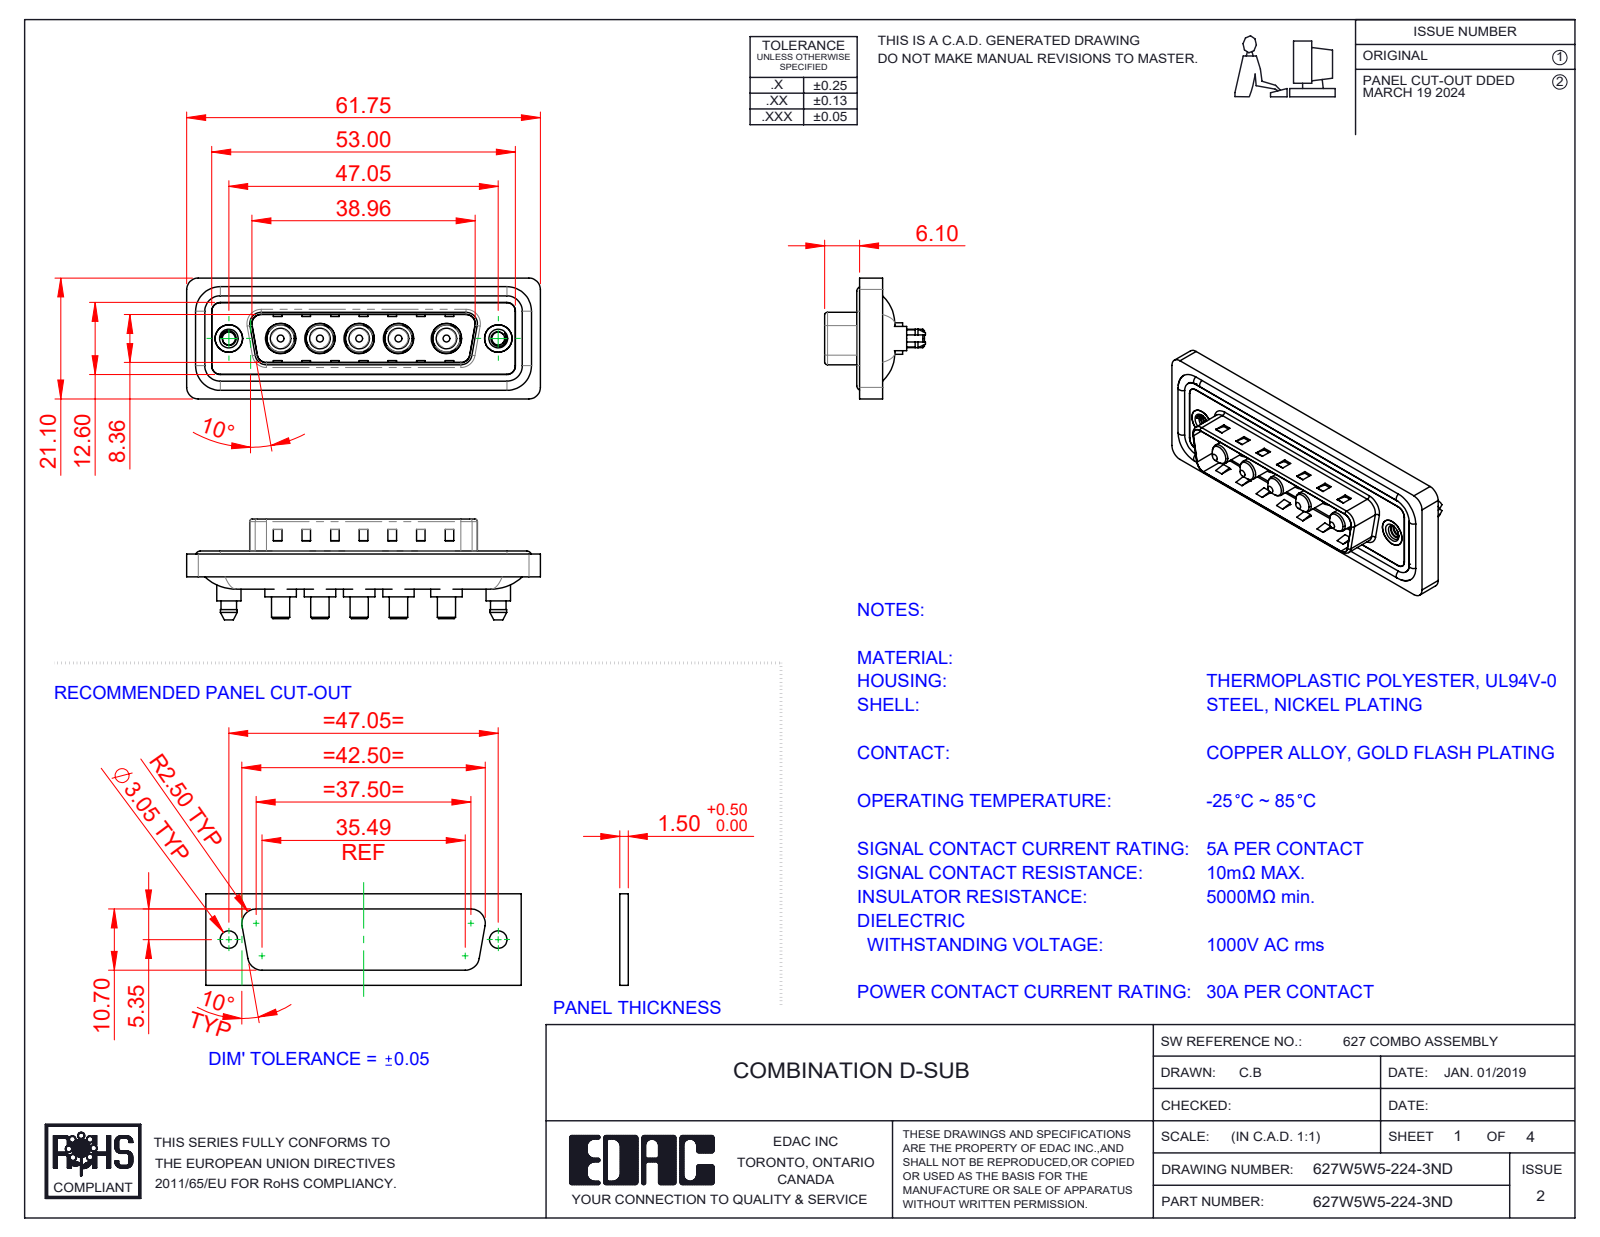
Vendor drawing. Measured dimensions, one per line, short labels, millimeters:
name: 627Combo Housing_5W5; 627Combo Threaded Boardlock_D; 627Combo Shell Front_25 Contacts; Power Pin_30A S (+4 more)
written by: SolidWorks 2023 (CONFIG_CONTROL_DESIGN)
unit: mm
bodies: 17 solids, 736 faces (275 planar, 323 cylindrical, 138 other)
size: 61.75 × 21.1 × 17.6
volume: 7 643 mm³; area: 12 155 mm²
holes: 5× ⌀4.85, 5× ⌀5.3, 2× ⌀2.26, 2× ⌀4, 2× ⌀4.8, 2× ⌀5
bosses: 5× ⌀5.5, 5× ⌀5.2, 5× ⌀4.75, 5× ⌀3.75, 5× ⌀3.6, 5× ⌀3.2, 4× ⌀1.6, 2× ⌀5.4
rounds: 24× R1.5, 18× R2, 10× R1.6, 8× R0.5, 5× R2.1, 4× R0.25, 4× R0.6, 4× R0.65
face distances: 0.4, 1.5, 3.1, 1.1, 0.5, 1.6, 2.9, 0.82, 9.58, 5.65
hole spacings: 6.86, 9.04, 13.73, 38.01, 6.87, 8.37, 8.38, 9.05
